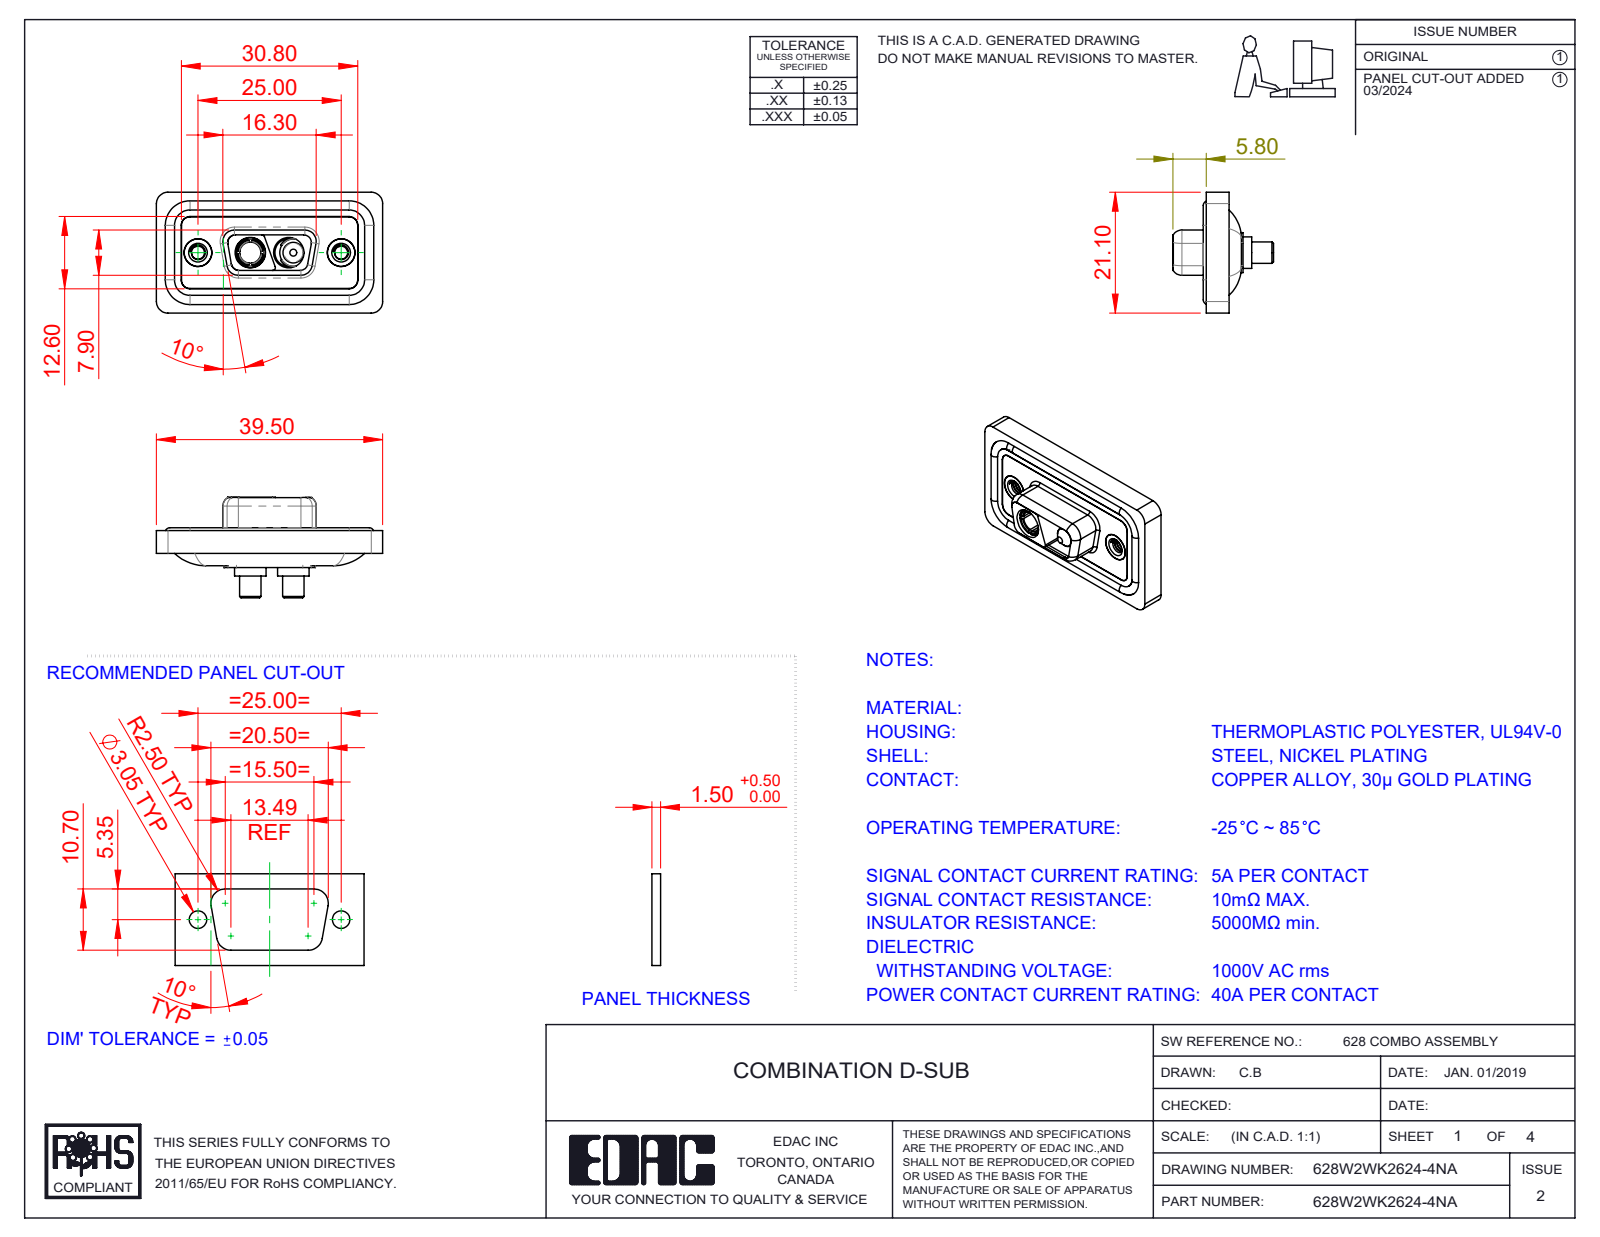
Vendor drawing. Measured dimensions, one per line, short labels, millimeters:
name: Power Pin_40A S; 628Combo Shell Rear_09 Contacts; 628Combo Housing_2WK2; 628Combo Shell Front_09 Contacts (+4 more)
written by: SolidWorks 2023 (CONFIG_CONTROL_DESIGN)
unit: mm
bodies: 11 solids, 498 faces (144 planar, 233 cylindrical, 121 other)
size: 39.5 × 21.1 × 17.55
volume: 4 642 mm³; area: 7 363 mm²
holes: 4× ⌀4.85, 2× ⌀2.26, 2× ⌀4, 2× ⌀4.05, 2× ⌀5, 2× ⌀5.3, 1× ⌀3.7
bosses: 4× ⌀1.6, 2× ⌀5.5, 2× ⌀5.2, 2× ⌀4.95, 2× ⌀4.8, 2× ⌀4.75, 2× ⌀3.75, 1× ⌀4.96
rounds: 22× R1.5, 18× R2, 8× R1.35, 8× R1.6, 6× R0.5, 4× R0.25, 4× R0.6, 4× R0.65
face distances: 0.4, 1.1, 2.9, 1.6, 0.5, 1.8, 5.65, 5.35, 3.1, 1.5
hole spacings: 9.14, 15.86, 6.72, 25
